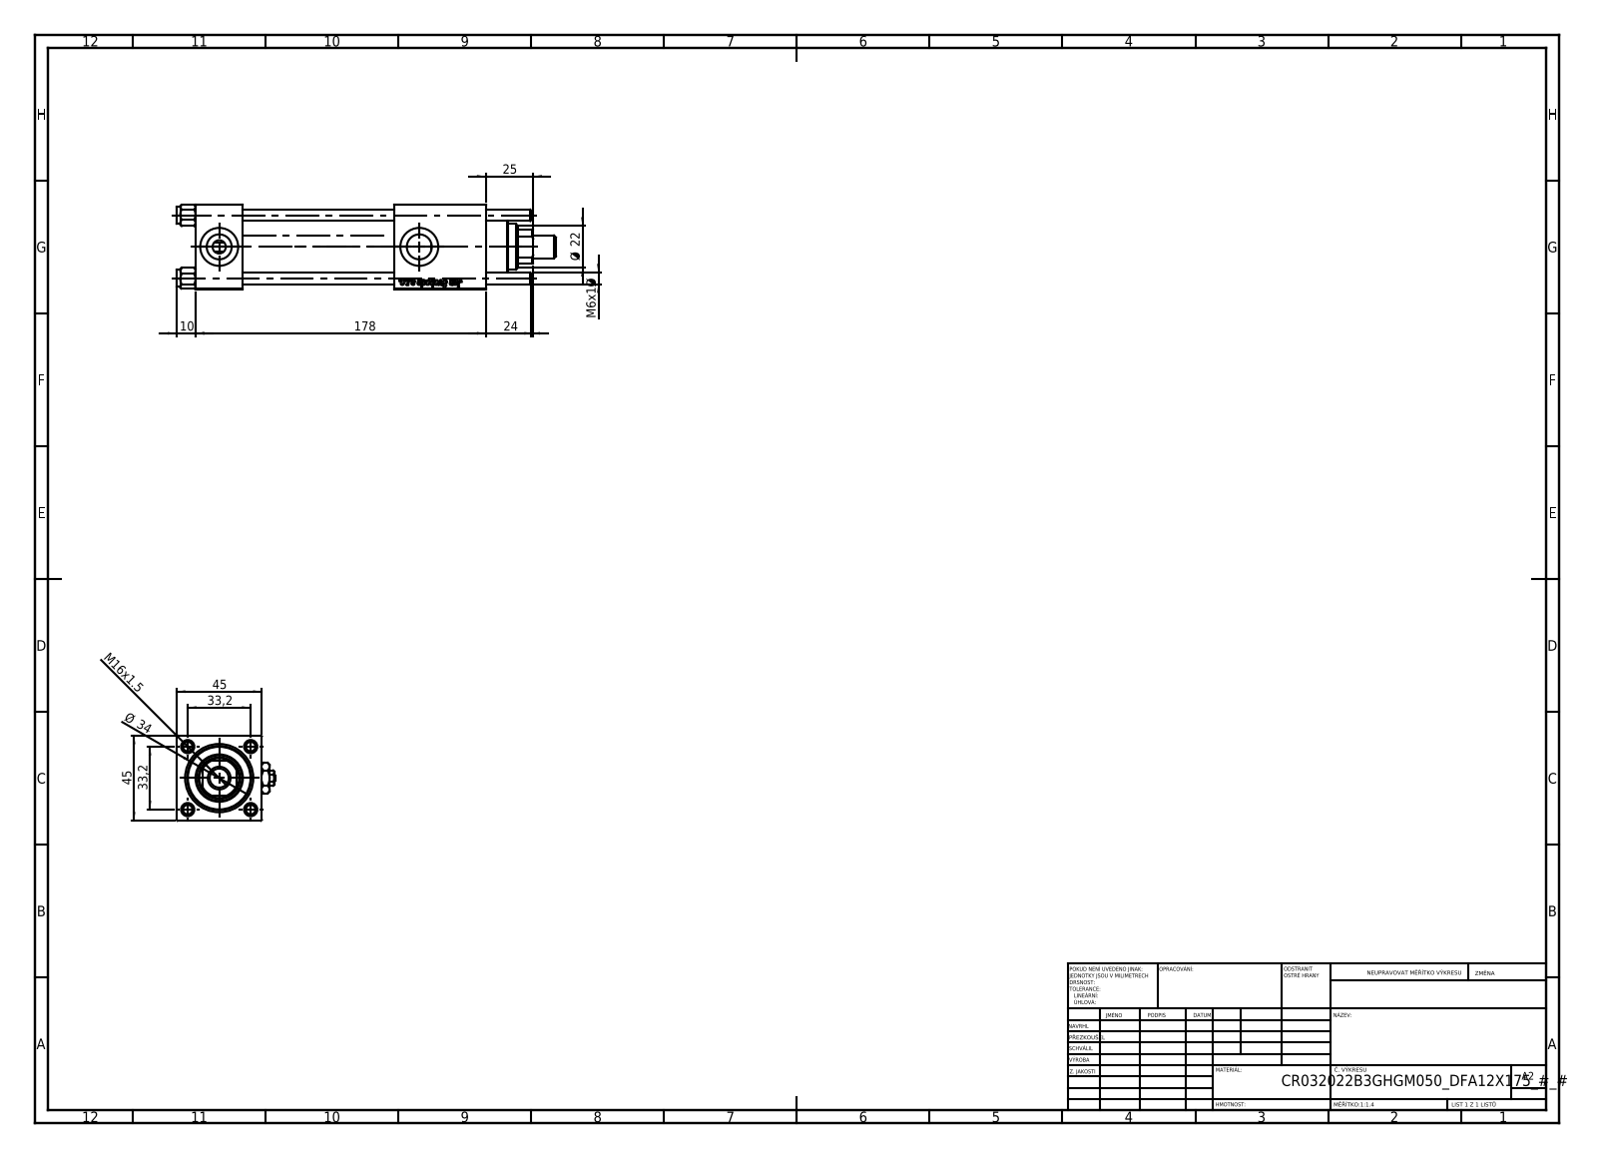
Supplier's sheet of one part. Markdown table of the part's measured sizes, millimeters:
| quantity | value |
| --- | --- |
| part name | NUT_M5_B; FEMALE_PART_FOR_DFA; Zatka_pro_OIL_PORT; V215_VC_A (+3 more) |
| STEP written by | SolidWorks 2019 (CONFIG_CONTROL_DESIGN) |
| units | millimeters |
| bodies | 14 solids, 1289 faces (490 planar, 97 cylindrical, 702 other) |
| overall size | 200 × 52 × 45 |
| volume | 247 286 mm³ |
| surface area | 93 986 mm² |
| round holes (diameter × count) | 6 × 4, 7 × 2, 13.16 × 2, 20 × 2, 10.5 × 1, 22 × 1, 24 × 1, 25 × 1, 32 × 1, 33 × 1 |
| round bosses / shafts (diameter × count) | 9 × 4, 38 × 1, 34 × 1, 28 × 1, 12 × 1, 10 × 1 |
| partial cylindrical surfaces (radius × count) | 9.75 × 1, 10.5 × 1 |
| main face-to-face distances | 45, 25, 153, 105, 80, 44.8, 128, 48, 124.3, 99.3 |
| hole center spacings | 23.48, 33.2, 46.95, 105.5 |
